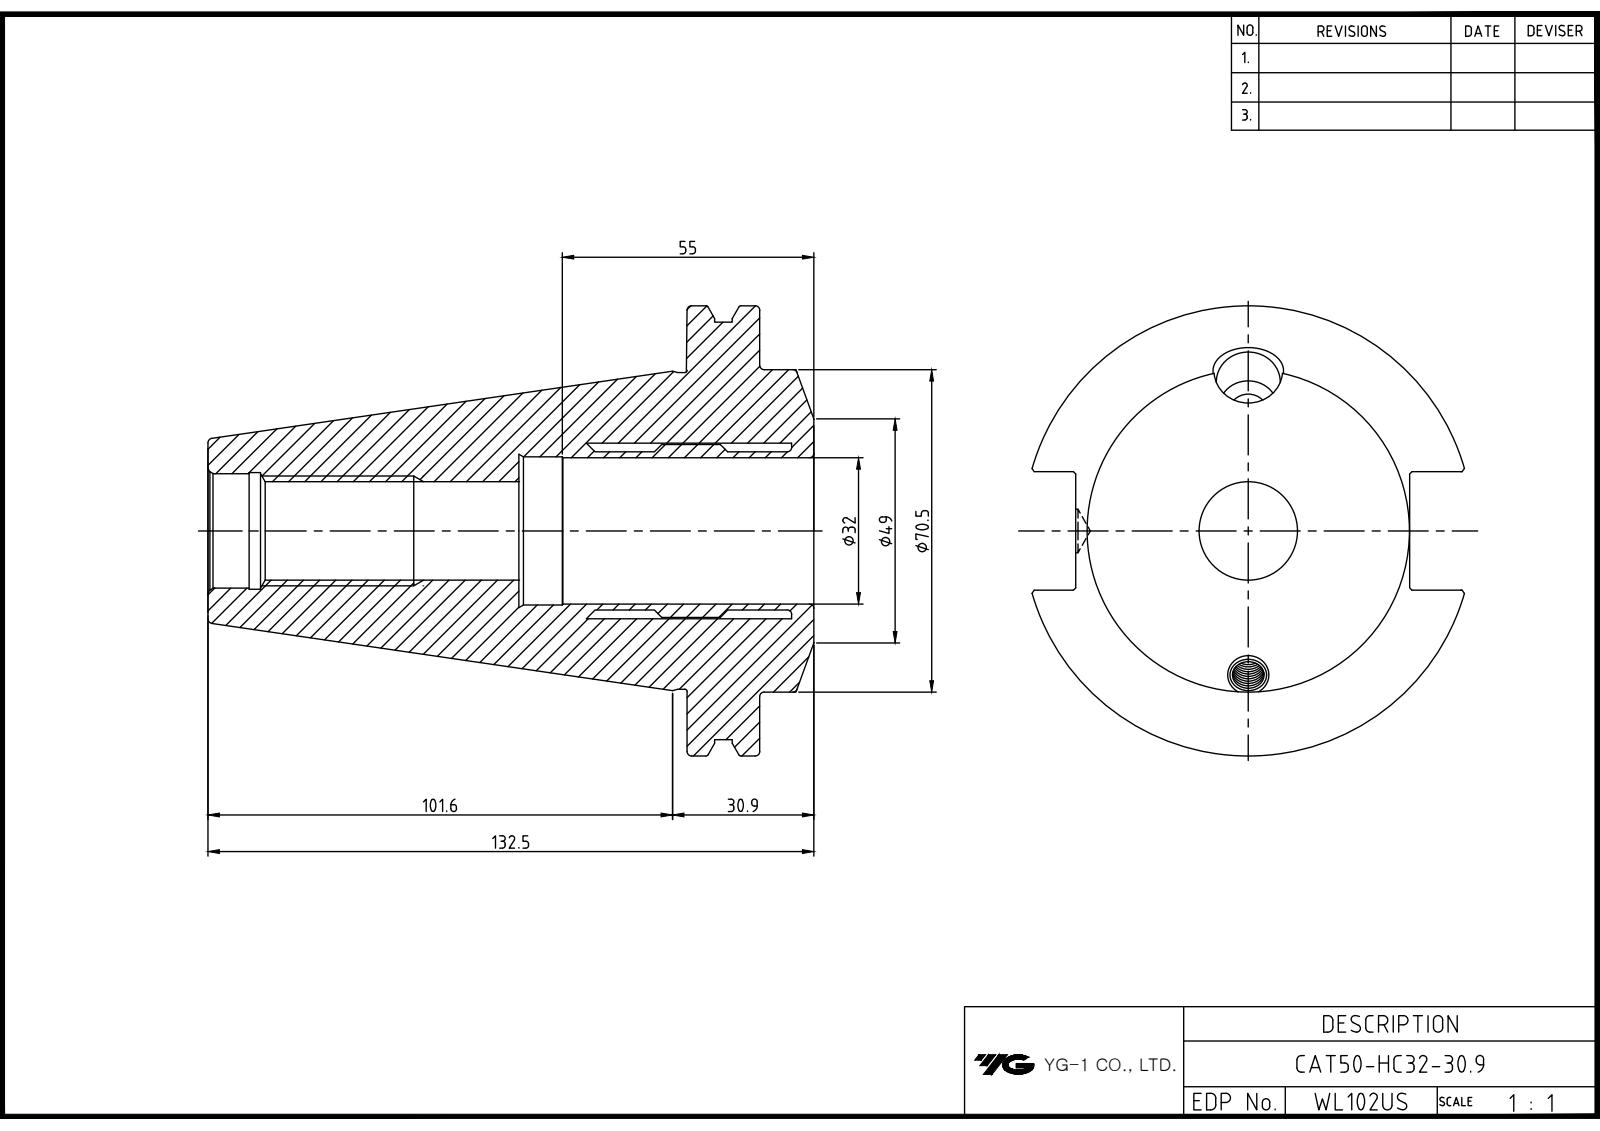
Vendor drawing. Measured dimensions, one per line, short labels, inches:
name: LO-CAT50-HC32-30.9
written by: Autodesk Inventor 2022 (AUTOMOTIVE_DESIGN)
unit: in
bodies: 1 solid, 57 faces (28 planar, 12 cylindrical, 17 other)
size: 5.217 × 3.875 × 3.728
volume: 20.17 in³; area: 74.8 in²
holes: 1× ⌀0.375, 1× ⌀0.865, 1× ⌀1.031, 1× ⌀1.26
bosses: 1× ⌀3.875, 1× ⌀3.594, 1× ⌀2.776, 1× ⌀2.726
face distances: 0.625, 1.092, 0.467, 4.125, 4.75, 5.217, 2.815, 1.31, 1.935, 2.402
